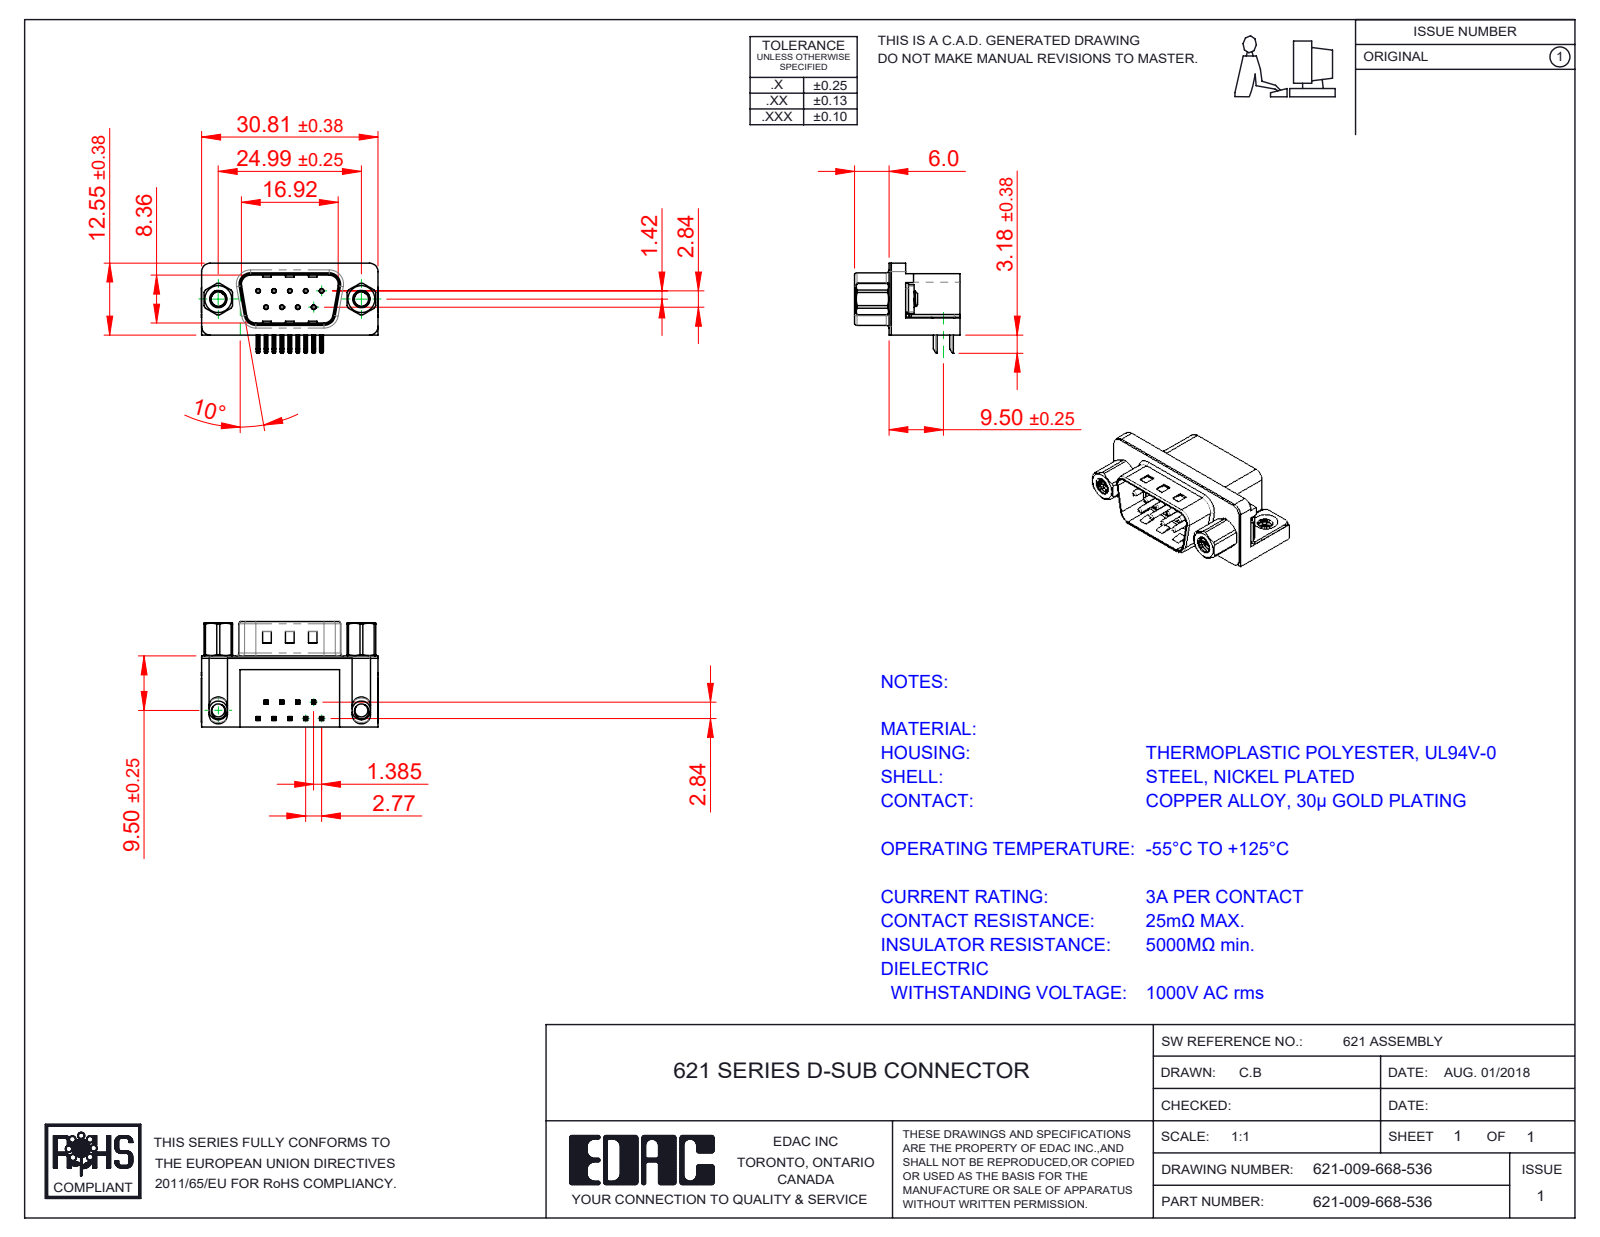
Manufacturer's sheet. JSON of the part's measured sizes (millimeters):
{"part_name": "621 2 Prong Board Lock; 621-009-668-536; 621 M3 Threaded Rivet; 621 Contact Top (+4 more)", "step_written_by": "SolidWorks 2016 (CONFIG_CONTROL_DESIGN)", "units": "millimeters", "bodies": {"solids": 17, "faces": 1179, "planar": 627, "cylindrical": 419, "other": 133}, "overall_size": [30.89, 18.4, 16.25], "volume_mm3": 3485, "surface_area_mm2": 4959, "round_holes": [[0.35, 9], [0.8, 9], [2.5, 2], [4, 2], [4.8, 2], [5, 2]], "round_bosses_or_shafts": [[0.75, 9], [4.9, 2], [4.75, 2], [3.9, 2], [3, 2]], "partial_cylinders_radius": [[0.25, 44], [0.12, 18], [1, 16], [0.5, 14], [1.5, 8], [1.6, 8], [0.32, 4], [0.9, 4]], "face_to_face_distances": [0.4, 12, 12.4, 10.35, 0.5, 9.5, 2.5, 2.9, 2.1, 0.35], "hole_center_spacings": [3.16, 2.77, 5.54, 5.03, 5.04, 8.31, 7.48, 7.49]}
